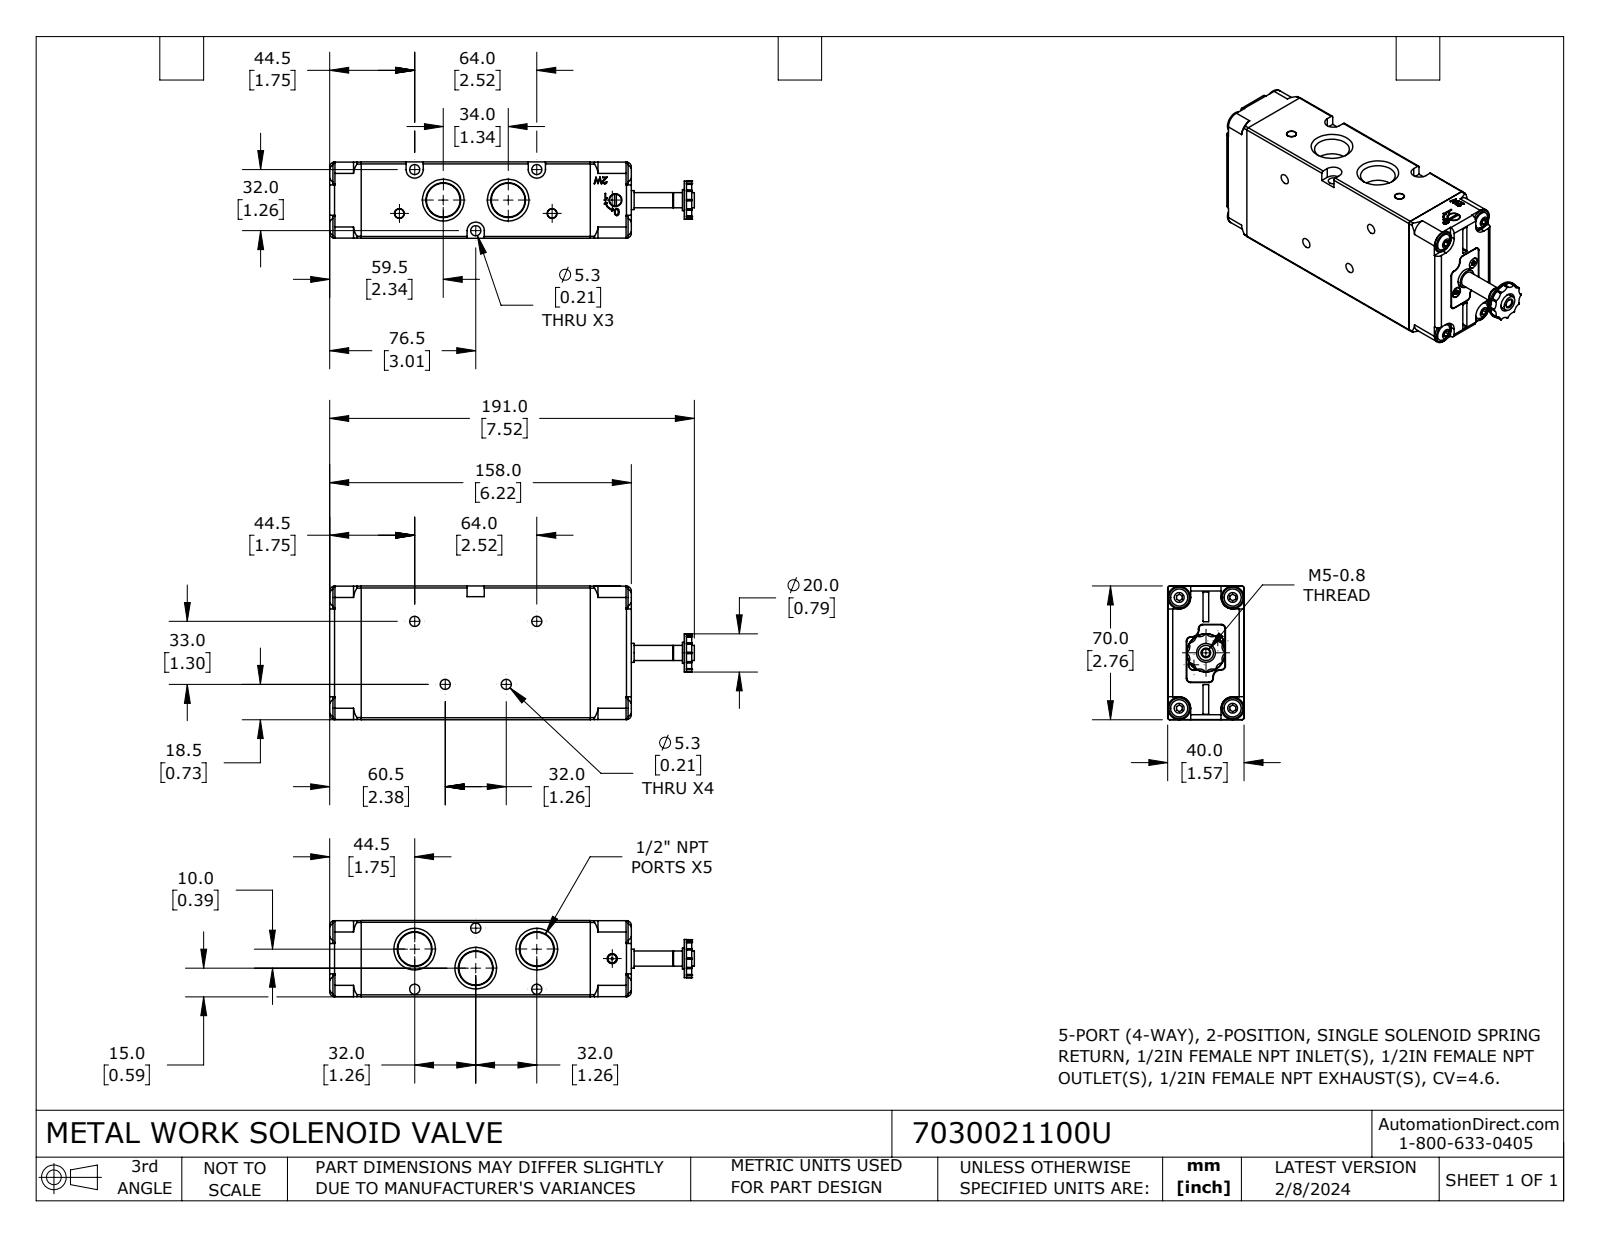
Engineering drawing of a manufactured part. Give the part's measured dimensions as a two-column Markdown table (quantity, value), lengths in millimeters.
| quantity | value |
| --- | --- |
| part name | 7030021100U |
| STEP written by | SolidWorks 2023 (CONFIG_CONTROL_DESIGN) |
| units | millimeters |
| bodies | 3 solids, 599 faces (258 planar, 247 cylindrical, 94 other) |
| overall size | 191 × 70.2 × 40 |
| volume | 417 100 mm³ |
| surface area | 62 780 mm² |
| round holes (diameter × count) | 5.3 × 7, 5.8 × 2, 4.1 × 1, 6.7 × 1, 10.2 × 1, 15 × 1 |
| round bosses / shafts (diameter × count) | 5.5 × 2, 4.8 × 2, 20 × 1, 19.9 × 1, 11 × 1, 10 × 1, 8 × 1, 7.6 × 1 |
| partial cylindrical surfaces (radius × count) | 0.2 × 12, 0.3 × 12, 0.5 × 12, 3.8 × 12, 0.3 × 8, 1 × 8, 2.5 × 8, 2 × 6 |
| main face-to-face distances | 40, 120, 39.9, 70, 21.5, 39.8, 69.9, 16.5, 136.5, 158 |
| hole center spacings | 8.8, 36.7, 45.2, 58.2, 64, 17.7, 32, 44.2 |
